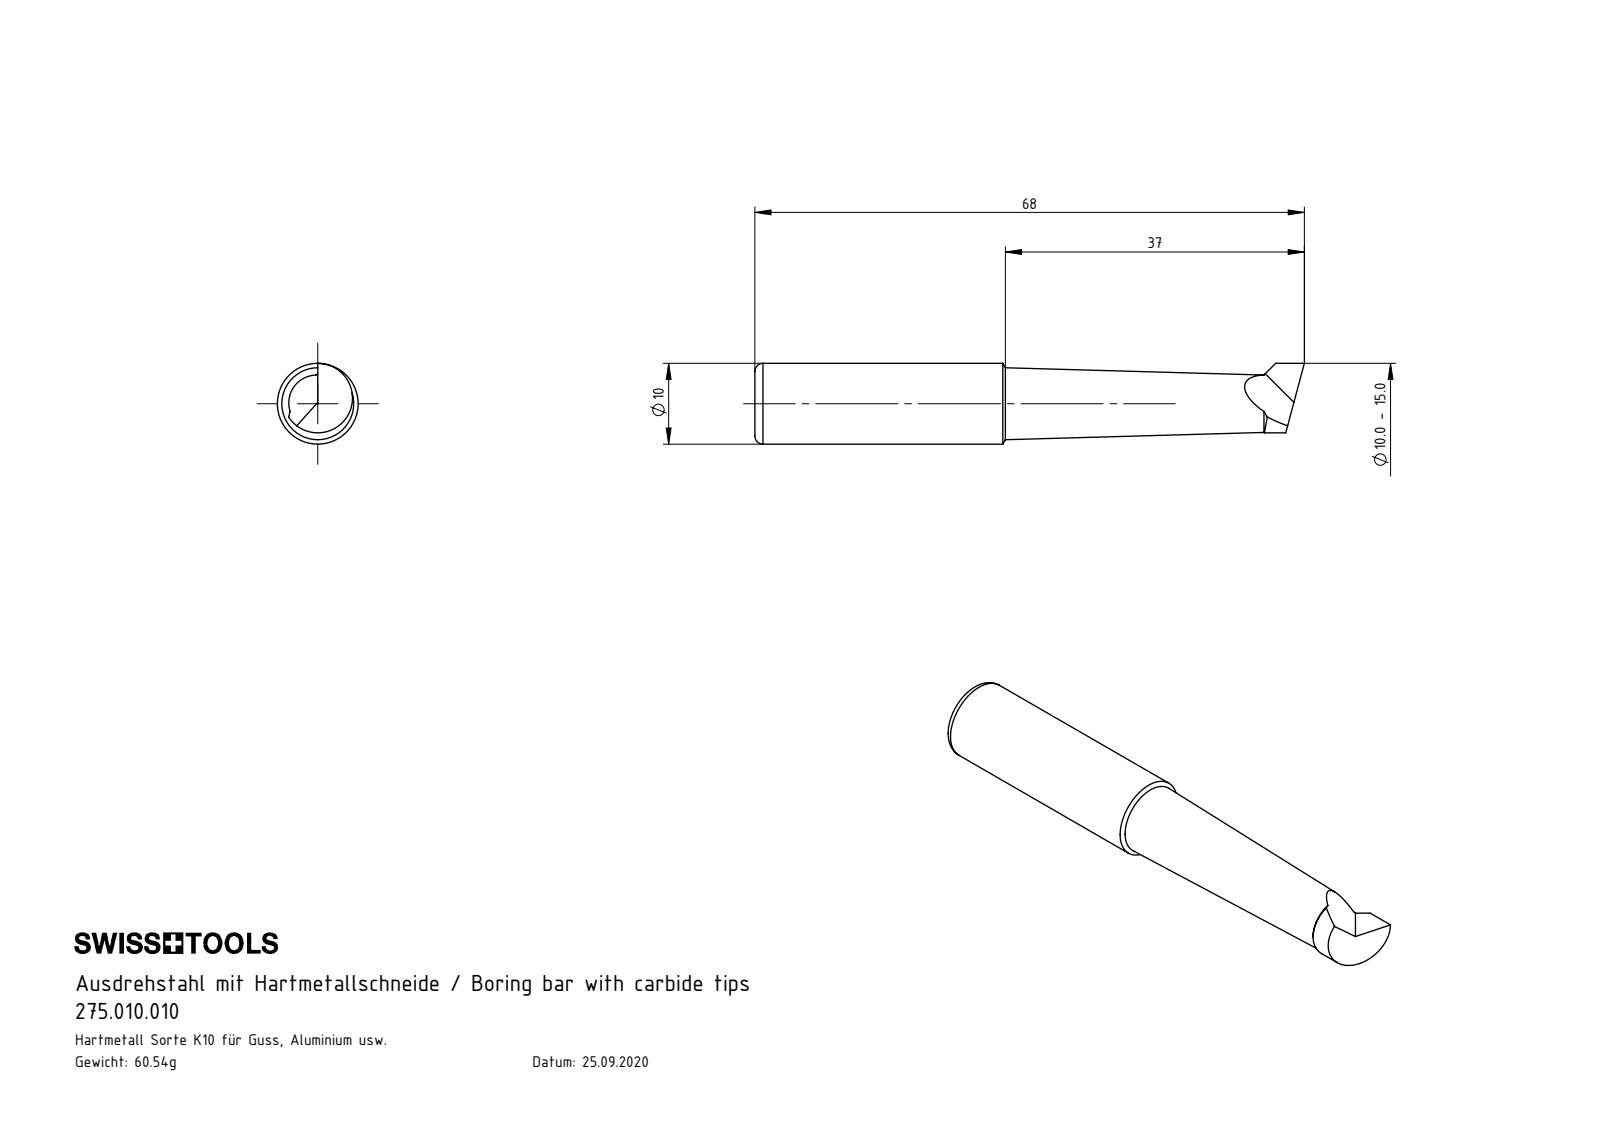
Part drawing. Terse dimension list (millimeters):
name: 275.010.010
written by: SolidWorks 2022 (CONFIG_CONTROL_DESIGN)
unit: mm
bodies: 1 solid, 16 faces (4 planar, 3 cylindrical, 9 other)
size: 68 × 10 × 10
volume: 4 175 mm³; area: 1 987 mm²
bosses: 1× ⌀10
rounds: 1× R4.3
